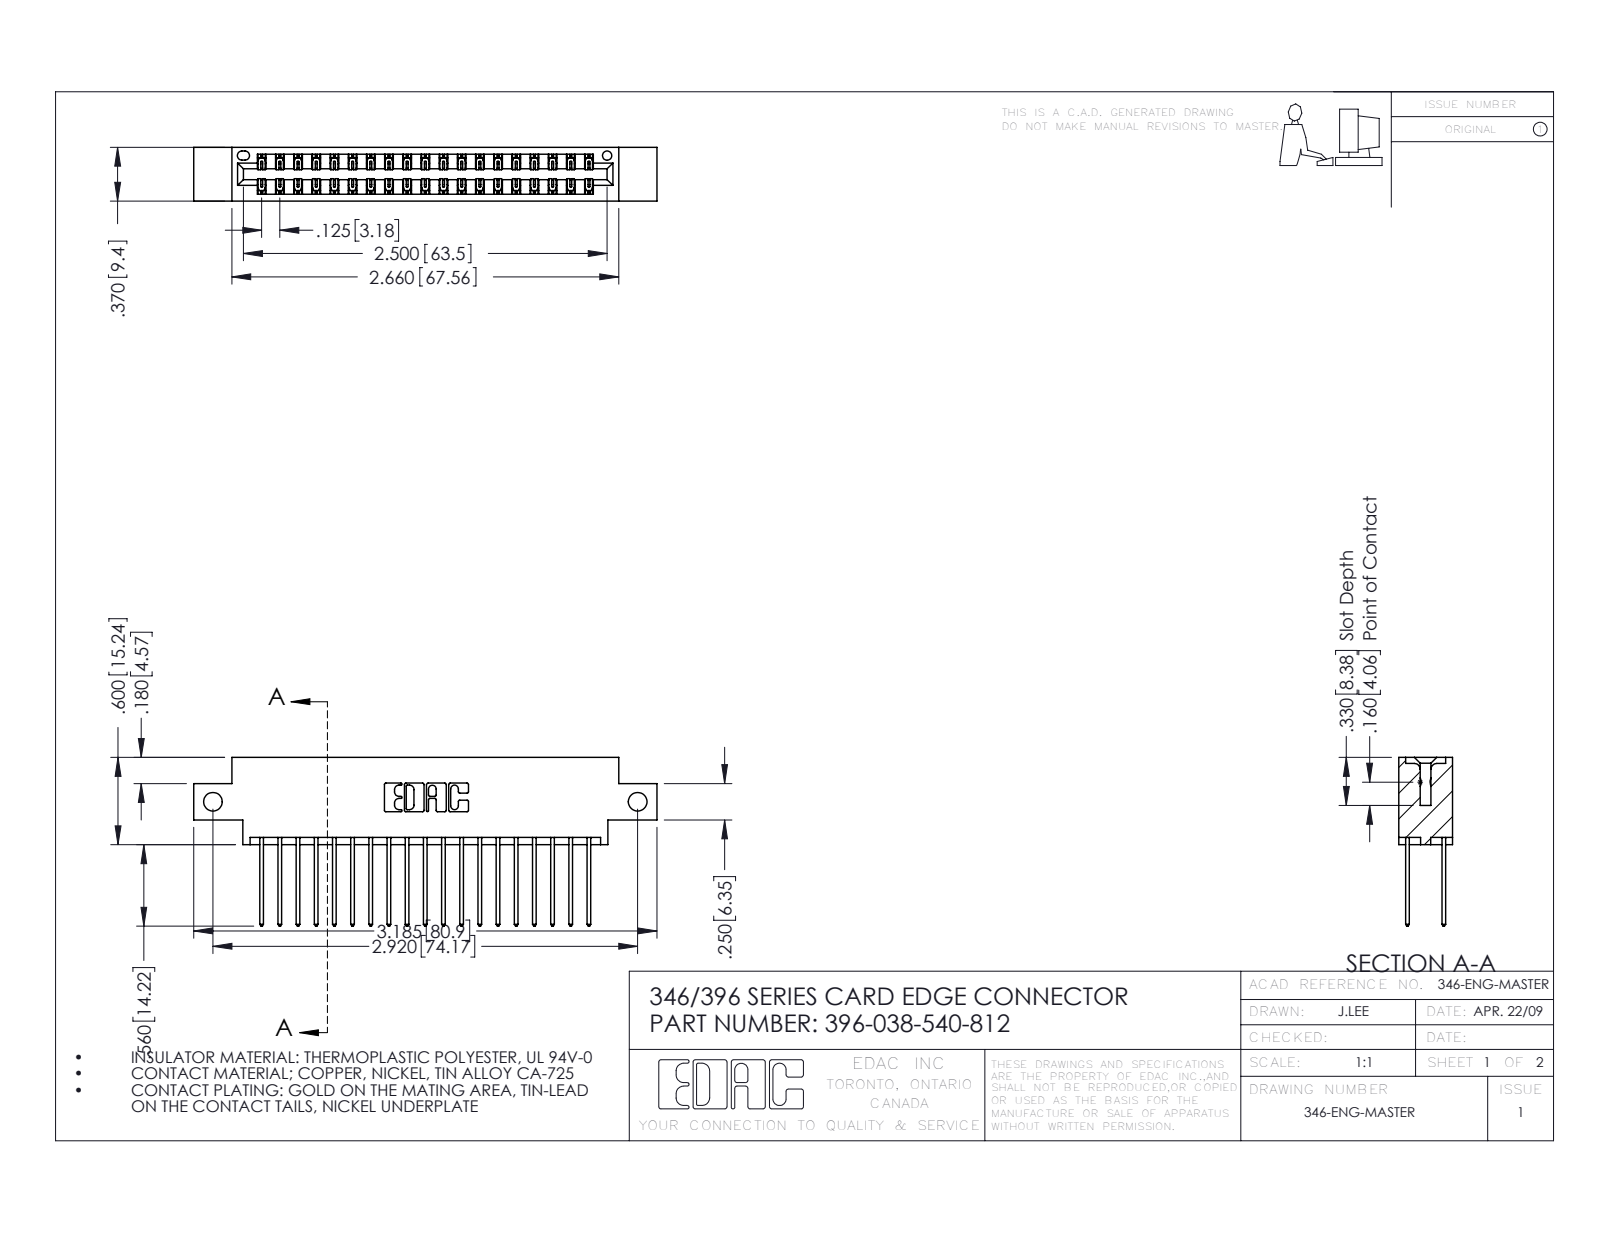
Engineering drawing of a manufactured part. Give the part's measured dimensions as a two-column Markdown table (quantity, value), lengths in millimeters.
| quantity | value |
| --- | --- |
| part name | 396-038-540-812; 345-292-001_345-293-140; 346 Part_0.170 Offset - Side Mount |
| STEP written by | SolidWorks 2016 (CONFIG_CONTROL_DESIGN) |
| units | millimeters |
| bodies | 39 solids, 2102 faces (1410 planar, 692 cylindrical, 0 other) |
| overall size | 80.9 × 29.5 × 9.4 |
| volume | 7 620 mm³ |
| surface area | 10 830 mm² |
| round holes (diameter × count) | 3.3 × 2, 1.6 × 1 |
| partial cylindrical surfaces (radius × count) | 0.2 × 57, 0.3 × 38, 0.3 × 22, 0.2 × 6, 0.8 × 6, 0.7 × 3, 0.4 × 2, 0.6 × 2 |
| main face-to-face distances | 1.2, 8.2, 6.4, 9.4, 1.8, 7.6, 0.6, 7, 5.7, 3.8 |
| hole center spacings | 74.2 |
